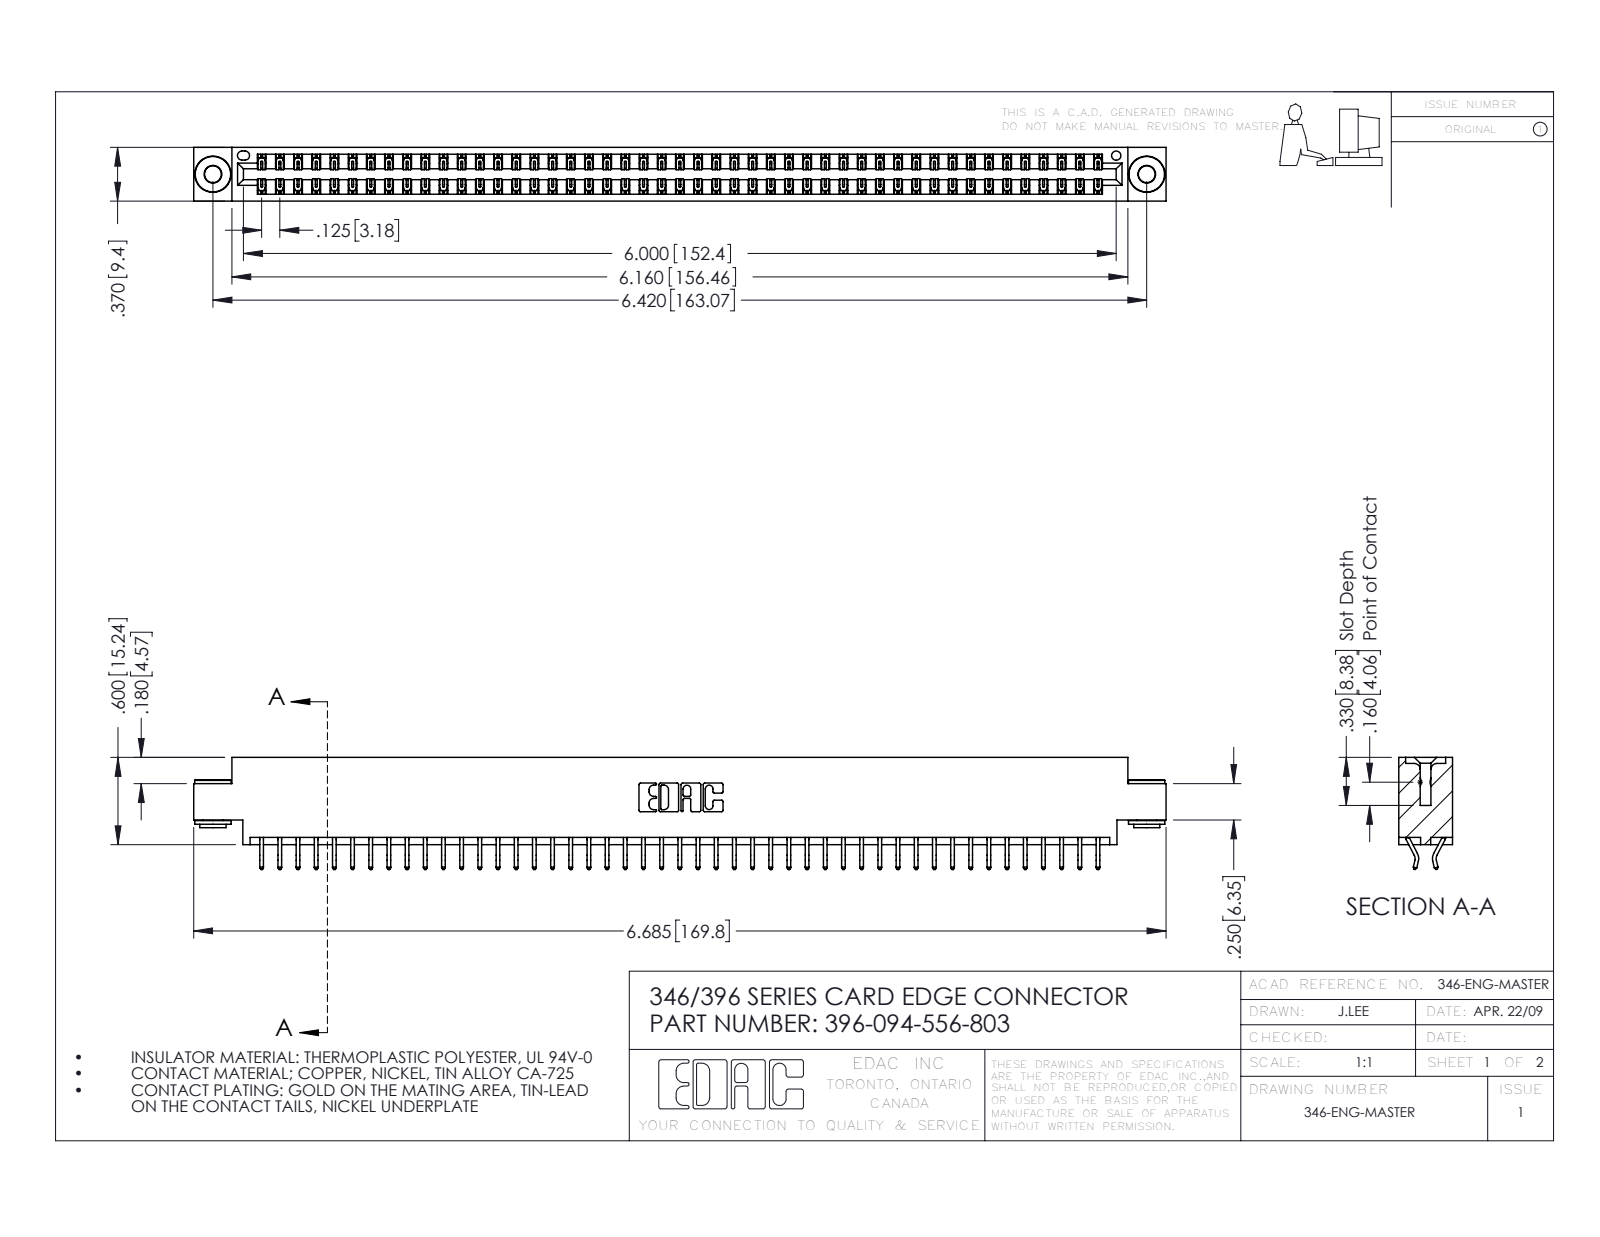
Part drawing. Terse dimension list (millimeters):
name: 396-094-556-803; 345-292-001_556 Tail; 346 Part_0.170 Offset - 0.156 Dia-TH; 345-250-002_345-250-002-102
written by: SolidWorks 2016 (CONFIG_CONTROL_DESIGN)
unit: mm
bodies: 97 solids, 5616 faces (3756 planar, 1852 cylindrical, 8 other)
size: 169.8 × 19.6 × 9.4
volume: 16 450 mm³; area: 23 010 mm²
holes: 2× ⌀2.9, 2× ⌀4, 1× ⌀1.6
bosses: 2× ⌀6.4, 2× ⌀4.6, 2× ⌀3.5
rounds: 141× R0.2, 22× R0.3, 6× R0.2, 6× R0.8, 3× R0.7, 2× R0.3, 2× R0.4, 2× R0.6
face distances: 1.2, 8.2, 9.4, 6.4, 0.6, 7, 1.8, 7.6, 3.8, 5.6
hole spacings: 6.2, 157.8, 163.1
